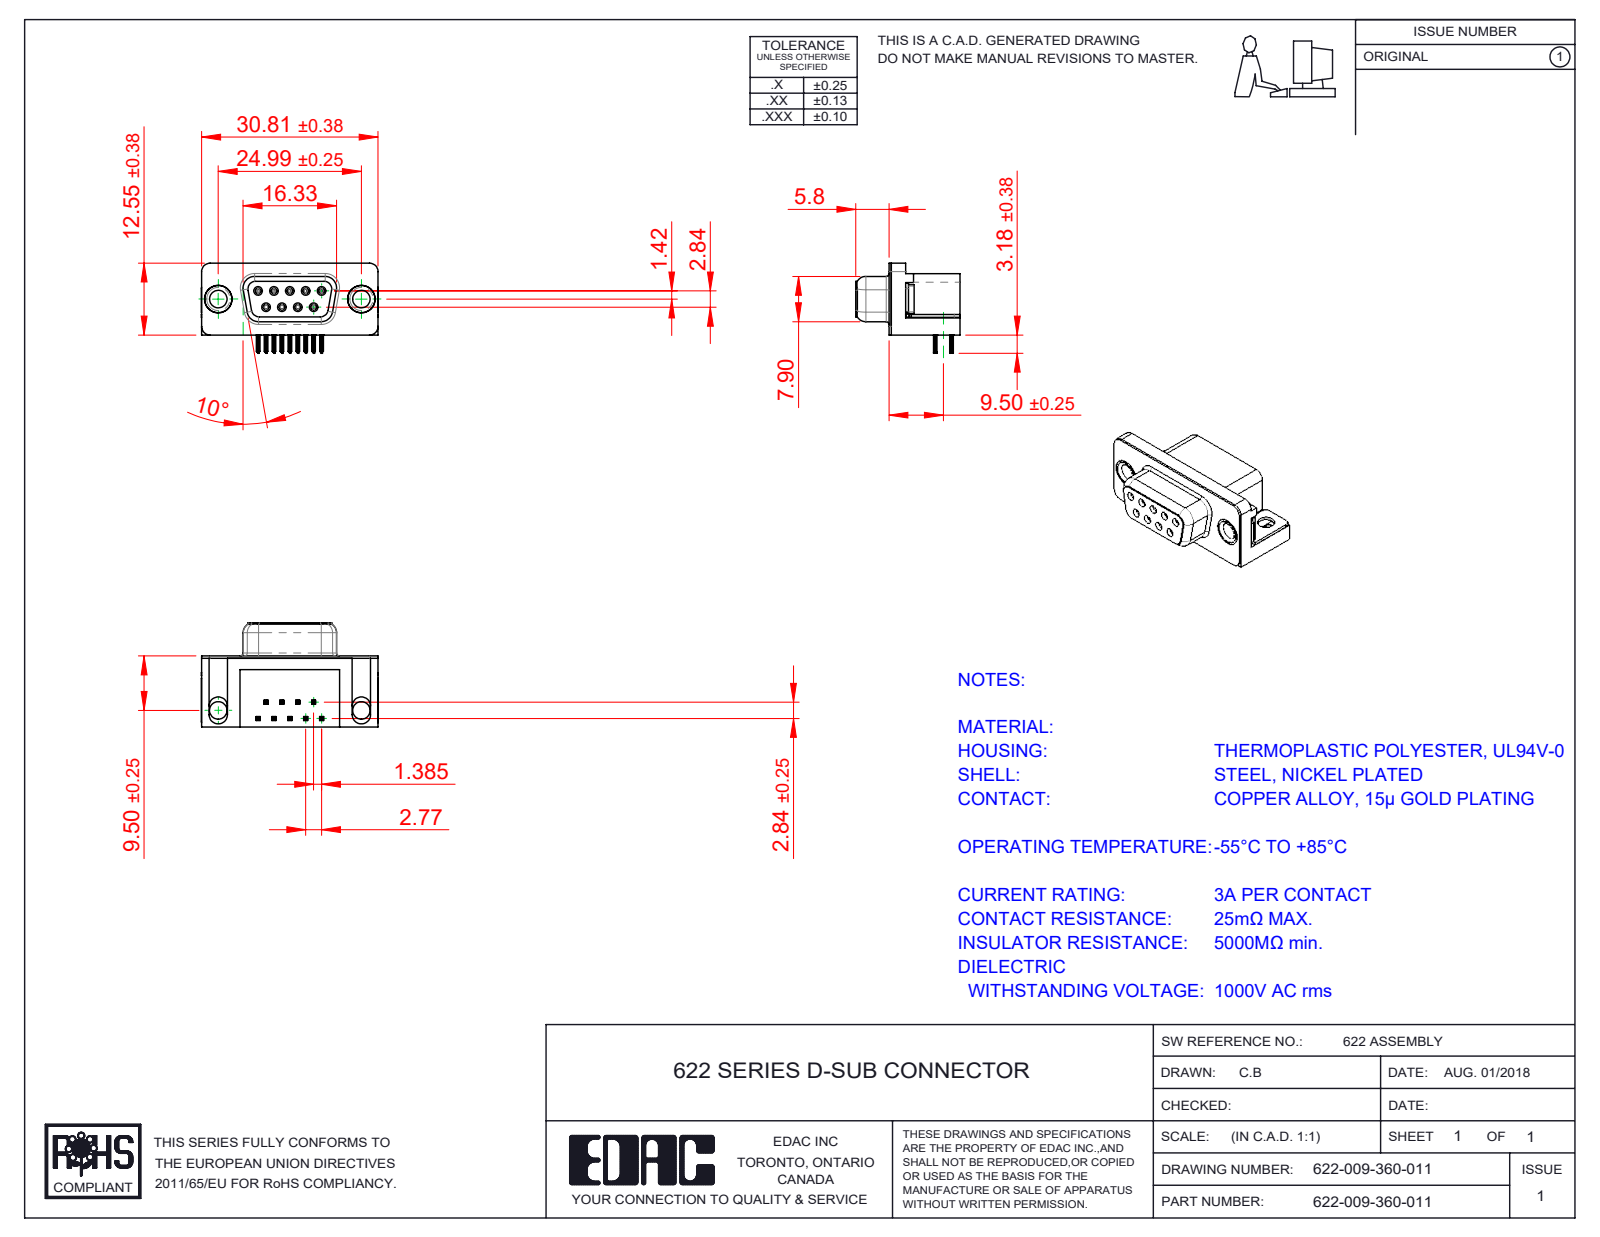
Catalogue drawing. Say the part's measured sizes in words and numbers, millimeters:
The part is named "622 Housing_9 Socket; 622 Socket Bottom; 622 Thru Hole Board Mount; 622-009-360-011 (+3 more)". Its 3-D file was written by "SolidWorks 2016 (CONFIG_CONTROL_DESIGN)". It is 15 solids with 1530 faces: 682 planar, 398 cylindrical and 450 other. Overall it measures 30.89 by 18.2 by 15.73 millimeters. Its volume is 3 711 cubic millimeters and its surface area 5 037 square millimeters. Round holes: 9 of diameter 0.8, 9 of diameter 0.9, 4 of diameter 3.05, 2 of diameter 4, 2 of diameter 4.8, 2 of diameter 5. Round bosses or shafts: 9 of diameter 1.2, 2 of diameter 4.9, 2 of diameter 4.75, 2 of diameter 3.85. Partial cylindrical surfaces (rounded edges, fillets, slot ends): 72 of radius 0.1, 36 of radius 0.15, 18 of radius 0.35, 18 of radius 1, 9 of radius 0.34, 8 of radius 0.25, 8 of radius 1.35, 8 of radius 1.6. The main face-to-face distances are 0.4, 12, 12.4, 0.35, 2.9, 2.5, 6.2, 10.34, 0.5, 9.5. The hole center spacings are 3.16, 2.77, 5.54, 5.03, 5.04, 8.31, 7.48, 7.49.
